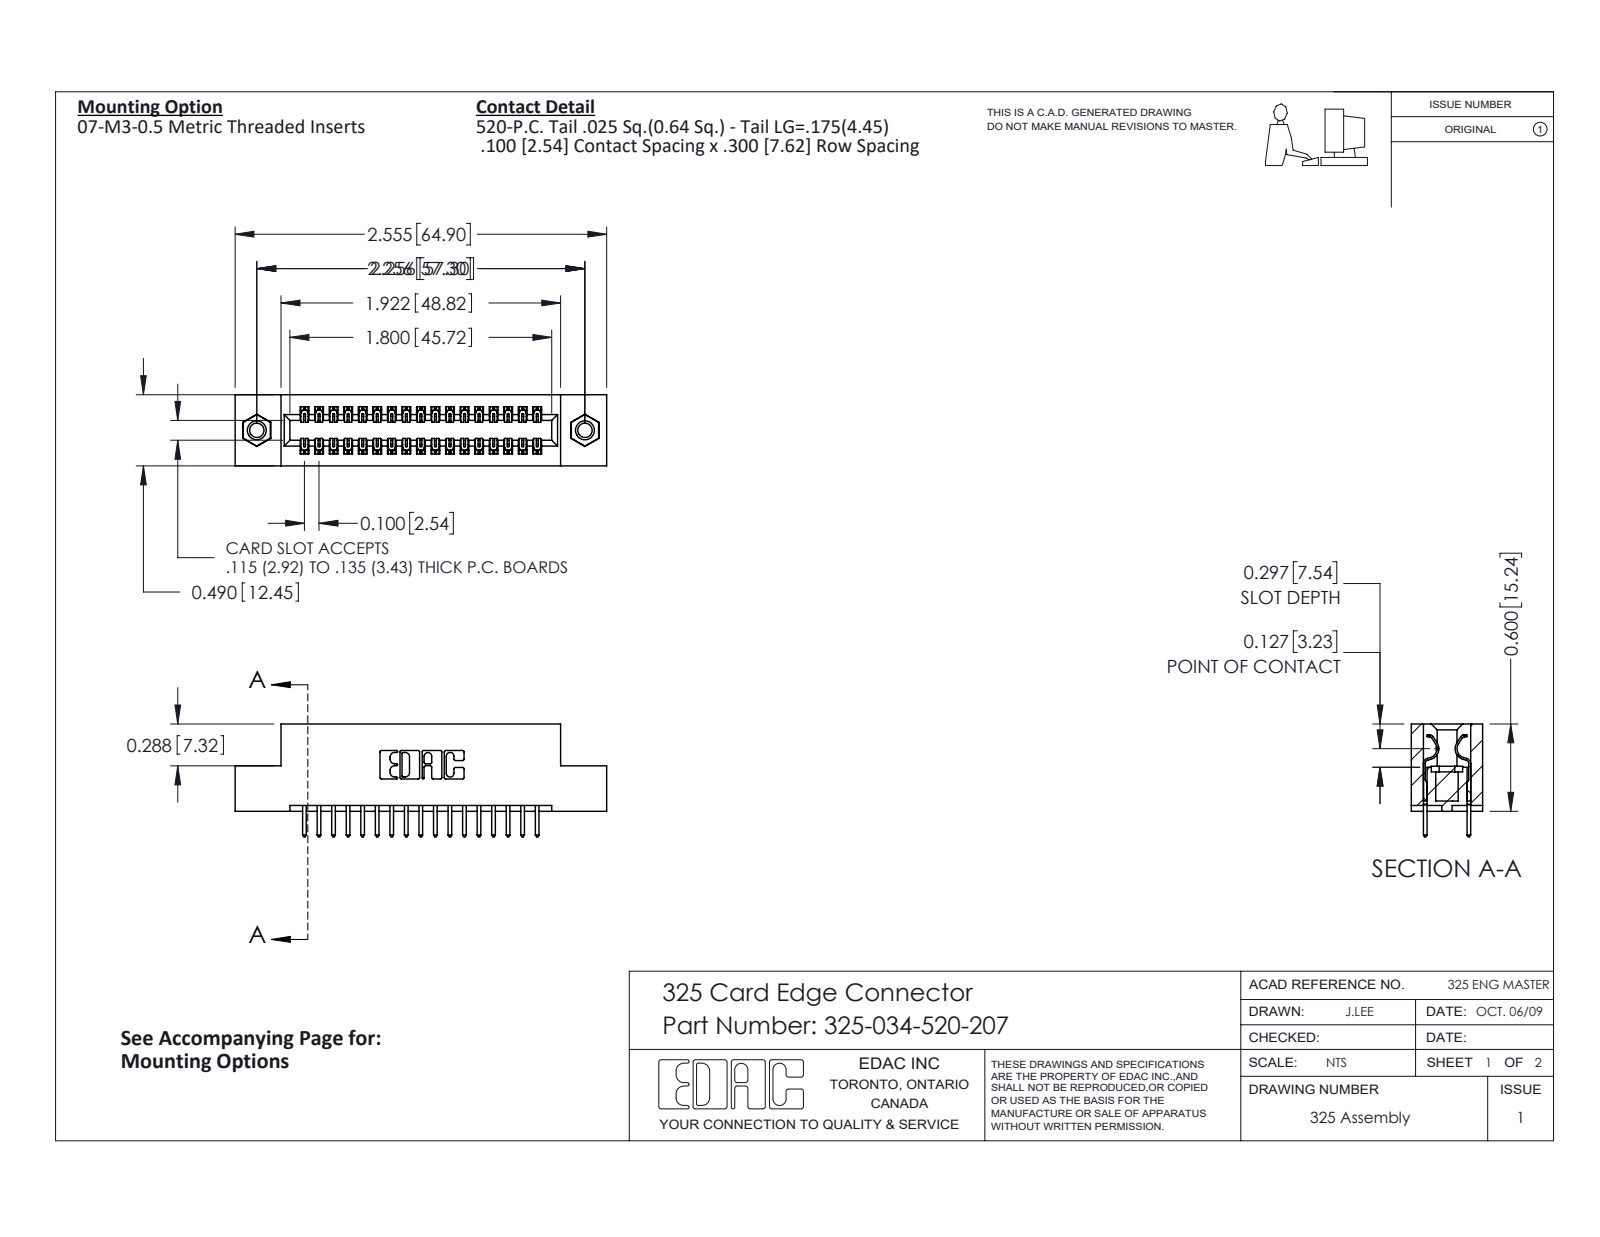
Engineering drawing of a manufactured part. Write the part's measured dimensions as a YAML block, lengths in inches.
part_name: "345-250-001_345-250-005-103; 325-034-520-207; 325 Part_TI; 325-292-001_325-293-120"
step_written_by: "SolidWorks 2016 (CONFIG_CONTROL_DESIGN)"
units: inches
bodies: {solids: 37, faces: 1942, planar: 1326, cylindrical: 600, other: 16}
overall_size: [2.555, 0.775, 0.49]
volume: 0.496
surface_area: 14.28
round_holes:
  - {diameter: 0.098, count: 2}
  - {diameter: 0.125, count: 2}
  - {diameter: 0.16, count: 2}
round_bosses_or_shafts:
  - {diameter: 0.155, count: 2}
partial_cylinders:
  - {radius: 0.006, count: 51}
  - {radius: 0.01, count: 34}
  - {radius: 0.01, count: 22}
  - {radius: 0.007, count: 6}
  - {radius: 0.031, count: 6}
  - {radius: 0.026, count: 3}
  - {radius: 0.014, count: 2}
  - {radius: 0.022, count: 2}
face_to_face_distances: [0.083, 0.407, 0.3, 0.49, 0.107, 0.383, 0.025, 0.325, 0.6, 0.04]
hole_center_spacings: [2.256]
